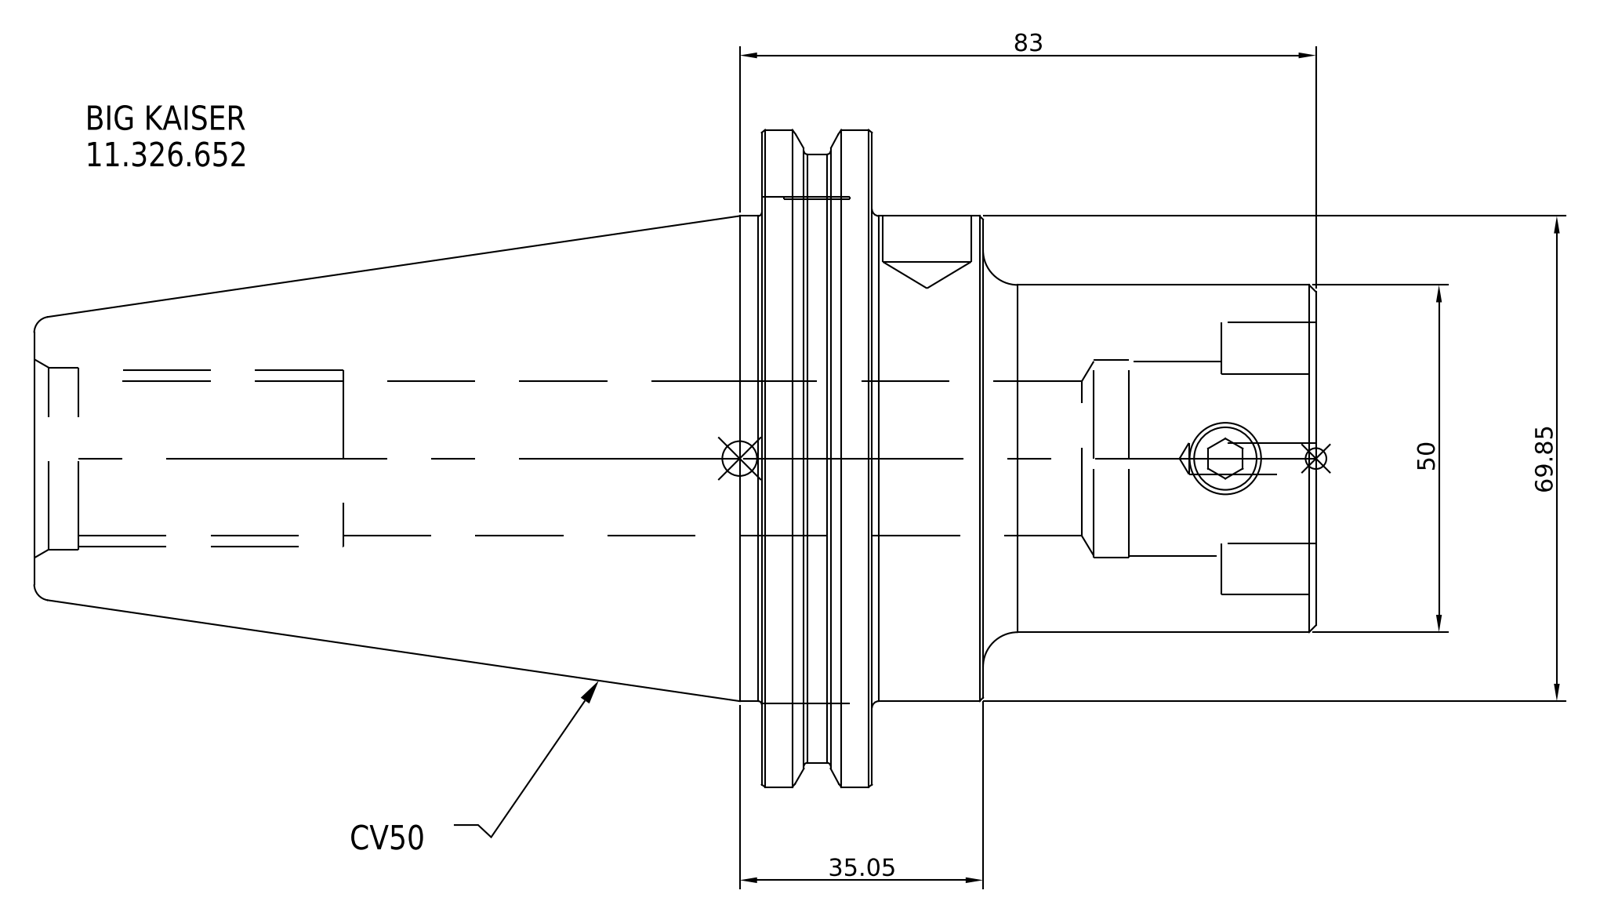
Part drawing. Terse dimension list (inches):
name: 11.326.652
written by: SolidWorks 2021 (CONFIG_CONTROL_DESIGN)
unit: in
bodies: 1 solid, 16 faces (7 planar, 6 cylindrical, 3 other)
size: 7.268 × 3.875 × 3.875
volume: 32.75 in³; area: 75.2 in²
bosses: 1× ⌀3.875, 1× ⌀3.594, 1× ⌀2.75, 1× ⌀1.969
face distances: 0.691, 2.518, 3.209, 1.89, 0.628, 1.319, 7.268, 5.378, 4.75, 4.059
